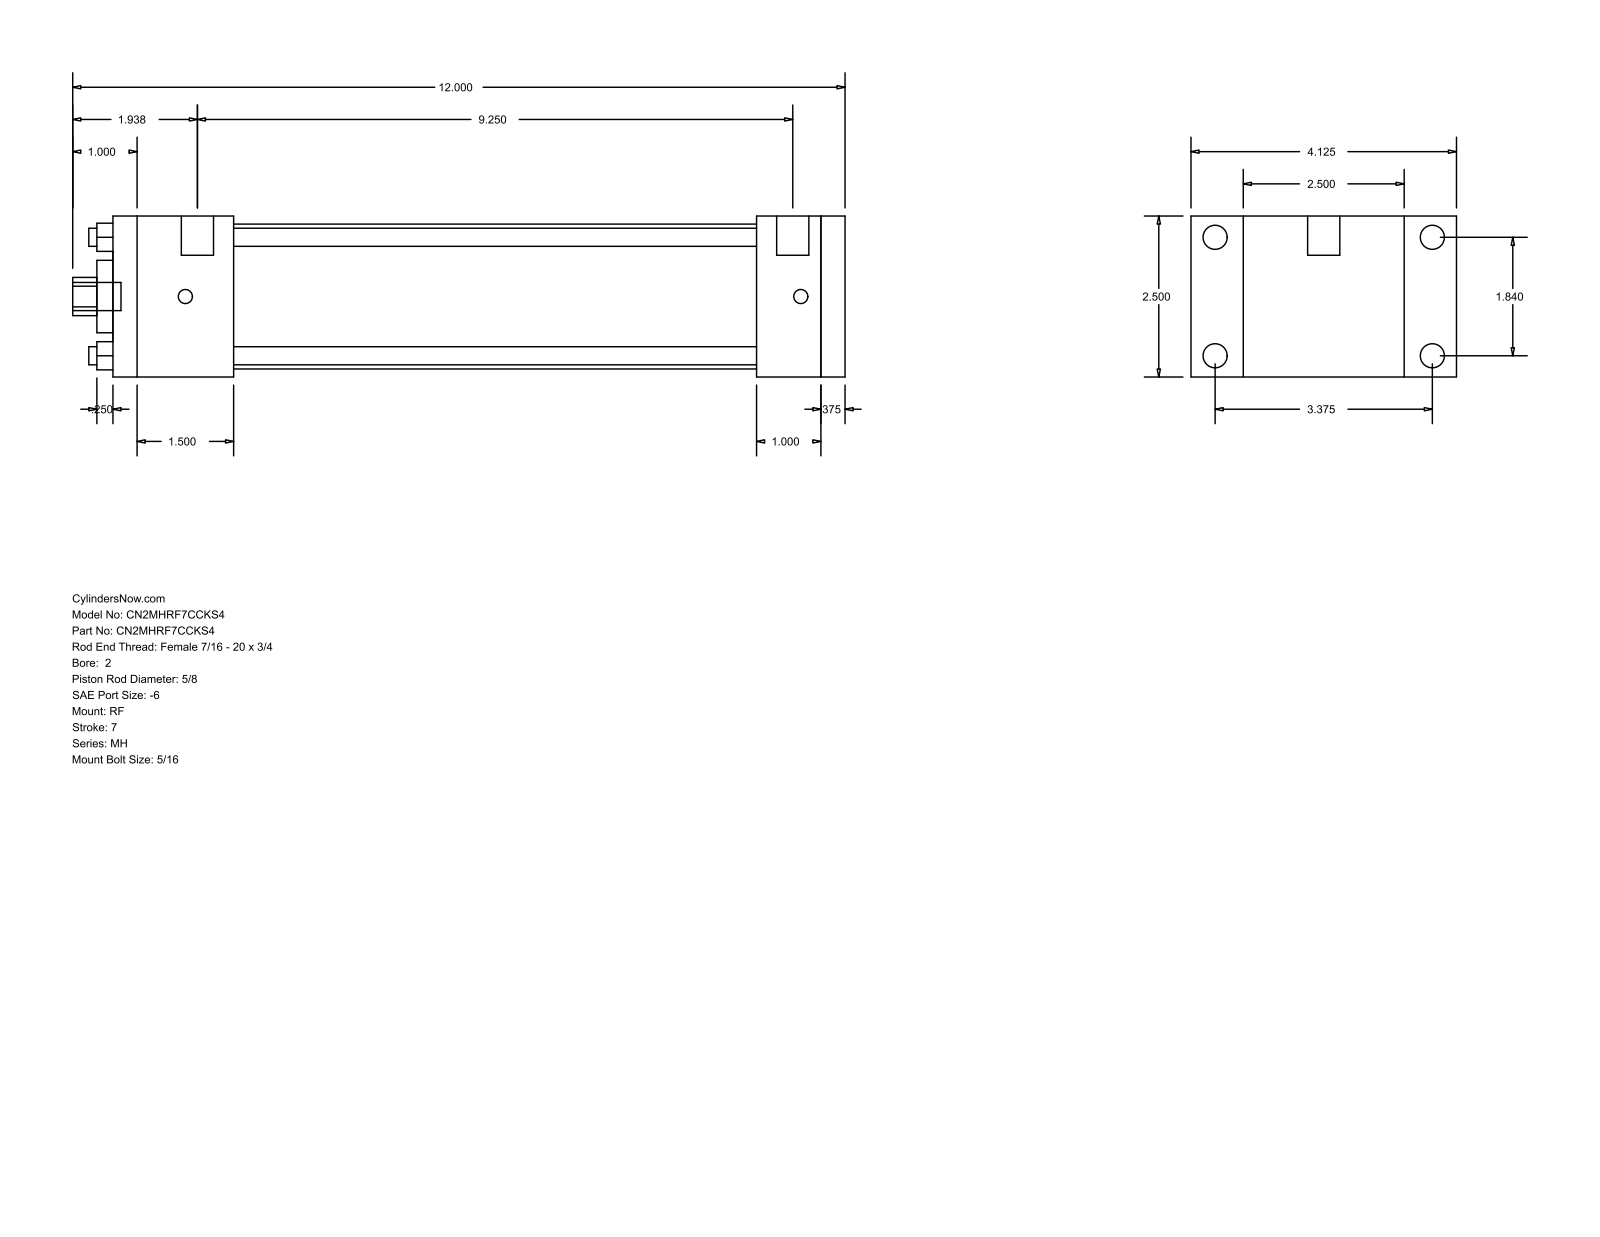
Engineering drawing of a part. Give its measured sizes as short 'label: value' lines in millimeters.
name: MH_RF__0200_0.625
written by: GSSL Pune (CONFIG_CONTROL_DESIGN)
unit: mm
bodies: 0 solids, 92 faces (64 planar, 28 cylindrical, 0 other)
size: 304.8 × 104.78 × 63.5
holes: 4× ⌀7.14, 1× ⌀15.88, 1× ⌀28.57, 1× ⌀57.15
bosses: 4× ⌀9.53, 4× ⌀5.56, 2× ⌀12.7, 1× ⌀11.11
rounds: 1× R7.54
face distances: 63.5, 288.92, 9.53, 279.39, 47.62, 254, 206.38, 231.77, 241.3, 25.39
hole spacings: 33.05, 46.74, 66.1
